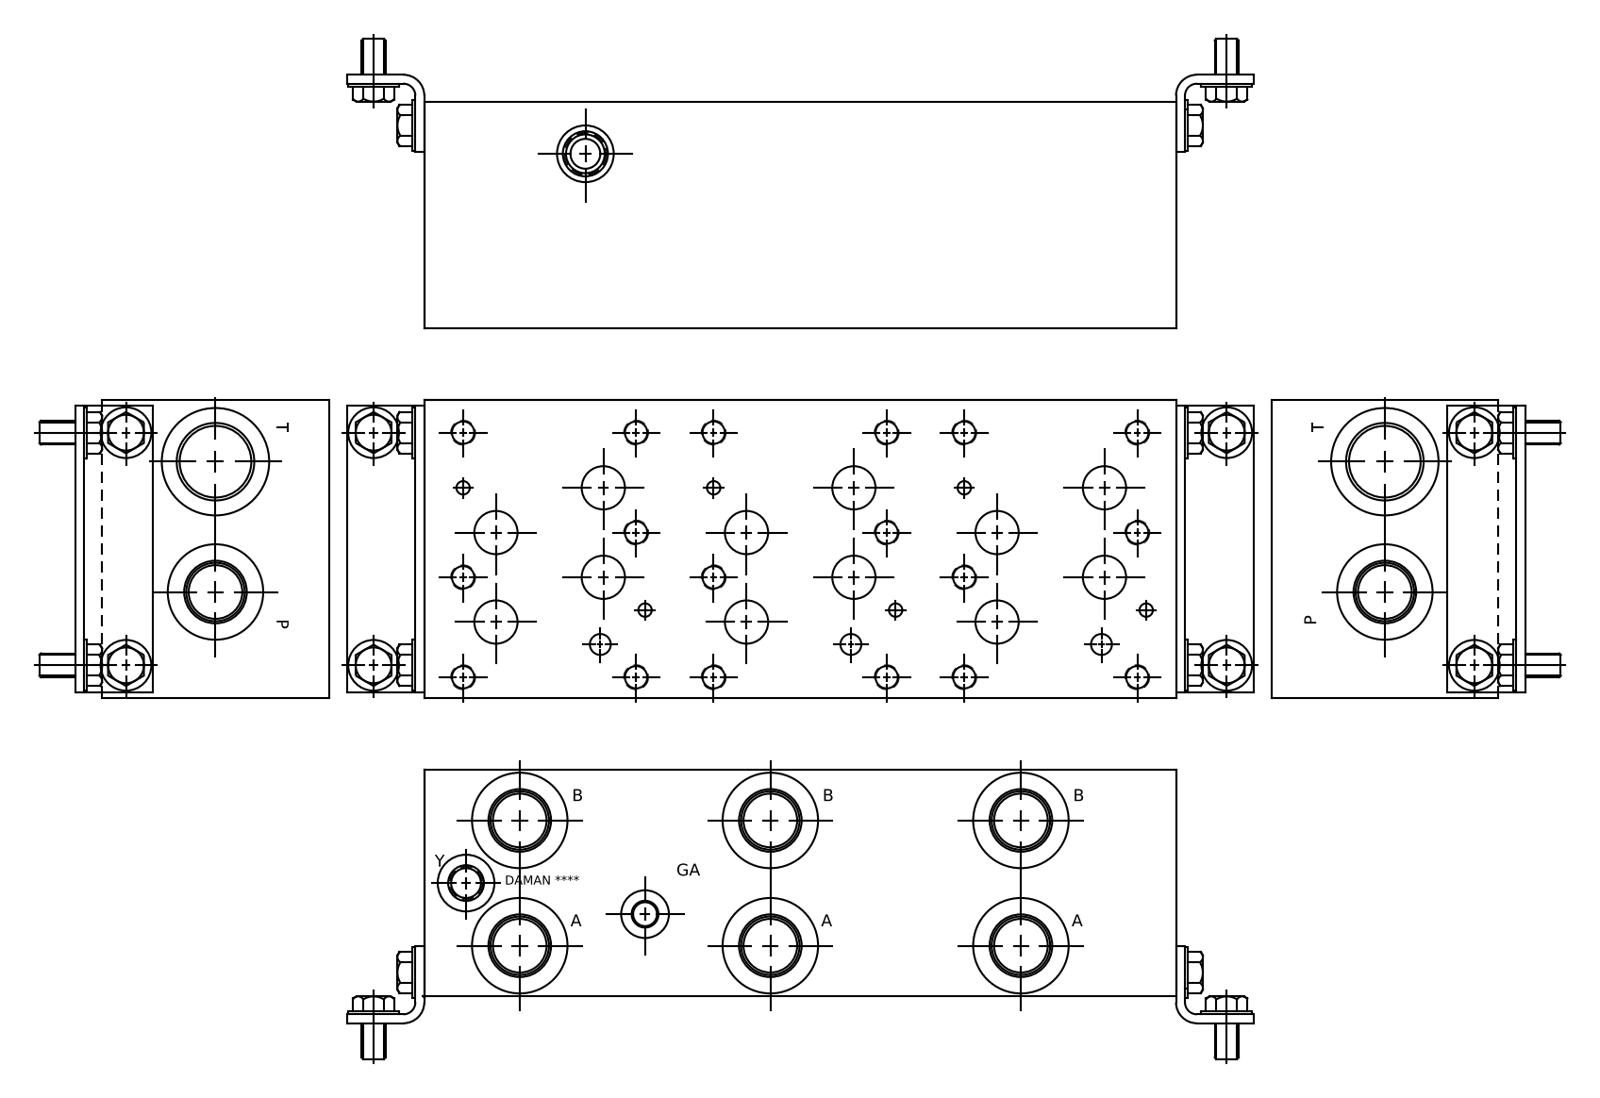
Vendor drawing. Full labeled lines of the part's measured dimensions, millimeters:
Part name (STEP PRODUCT): Part_AD08P035S_C_3D
STEP written by: Autodesk Inventor 2020 (AUTOMOTIVE_DESIGN)
Units: millimetres
Bodies: 1 solid, 862 faces (414 planar, 137 cylindrical, 311 other)
Overall size (bounding box): 400.05 × 158.75 × 120.65
Volume: 7 160 000 mm³ · Surface area: 343 176 mm²
Round holes (diameter × count): ⌀10.72 ×21, ⌀12.7 ×20, ⌀23.01 ×11, ⌀31.27 ×7, ⌀33.76 ×7, ⌀49.12 ×7, ⌀7.14 ×6, ⌀28.57 ×6, ⌀33.35 ×6, ⌀35.51 ×6, ⌀11.13 ×2, ⌀14.3 ×2
Main face-to-face distances: 120.65, 158.75, 400.05, 0.79, 157.96, 399.26, 398.47, 19.84, 19.05, 90.42
Hole centre spacings: 133.35, 266.7, 61.92, 74.63, 118.29, 152.7, 191.98, 29.53
